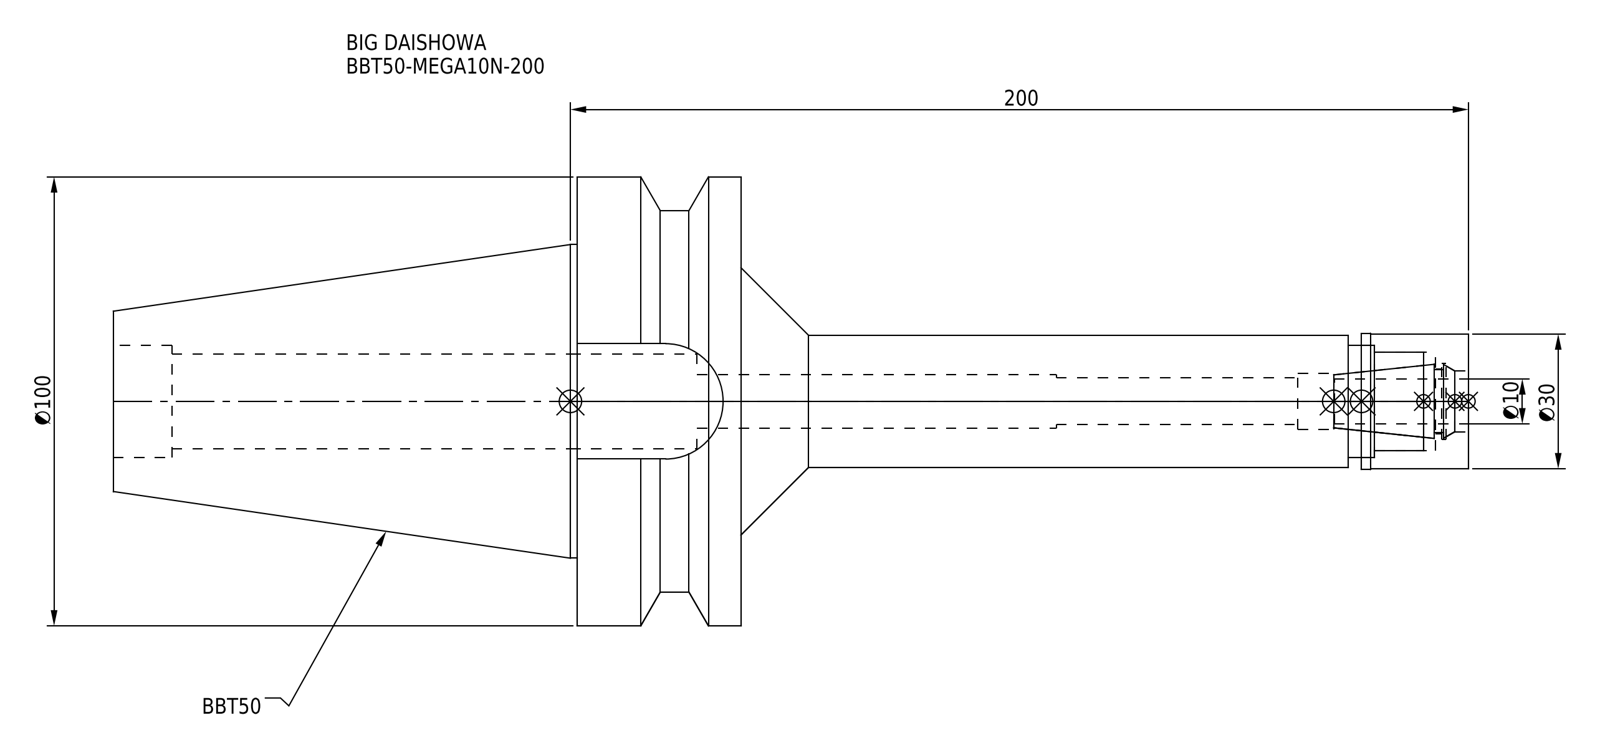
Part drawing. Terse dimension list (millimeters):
name: MGN10_1.stp; BBT50-MEGA10N-200_1.stp; BBT50-MEGA10N-200-100.stp; BBT50-MEGA10N-200 (+3 more)
written by: SolidWorks 2019 (CONFIG_CONTROL_DESIGN)
unit: mm
bodies: 2 solids, 79 faces (23 planar, 42 cylindrical, 14 other)
size: 301.8 × 100 × 100
volume: 556 101 mm³; area: 78 102 mm²
holes: 1× ⌀10.4, 1× ⌀12, 1× ⌀12.5, 1× ⌀13.5, 1× ⌀14.5, 1× ⌀17, 1× ⌀21.2, 1× ⌀22, 1× ⌀25
bosses: 1× ⌀100, 1× ⌀85, 1× ⌀69.85, 1× ⌀30.3, 1× ⌀30, 1× ⌀29.5
rounds: 1× R12.85
face distances: 36.5, 139.8, 103.3, 70.8, 162, 198.5, 301.8, 25.7, 171.8, 9.8
